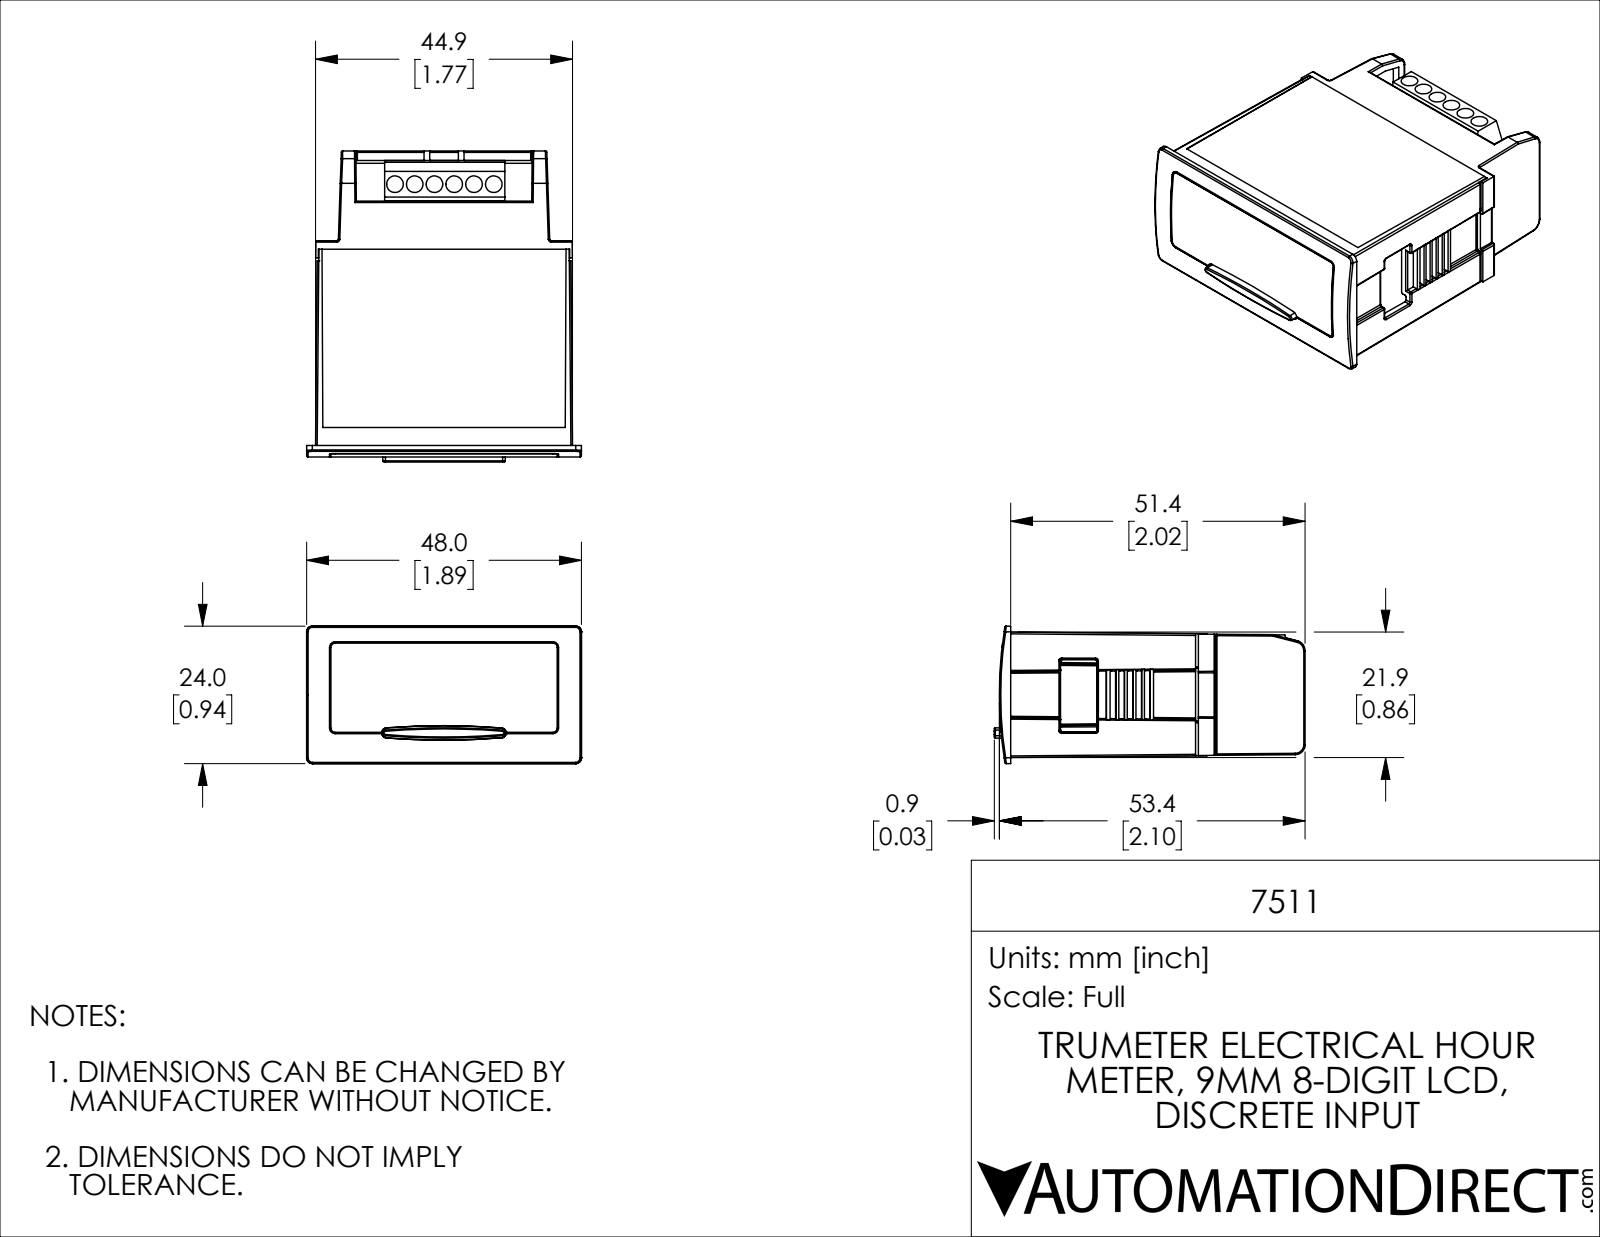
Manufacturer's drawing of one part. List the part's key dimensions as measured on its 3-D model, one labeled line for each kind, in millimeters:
Part name (STEP PRODUCT): 7511
STEP written by: SolidWorks 2021 (CONFIG_CONTROL_DESIGN)
Units: millimetres
Bodies: 2 solids, 1771 faces (1106 planar, 291 cylindrical, 374 other)
Overall size (bounding box): 54.3 × 48 × 24
Volume: 15 500 mm³ · Surface area: 21 700 mm²
Round holes (diameter × count): ⌀2.9 ×6
Round bosses / shafts (diameter × count): ⌀3.8 ×3, ⌀1.8 ×1
Partial cylindrical surfaces — rounded edges, fillets, slot ends (radius × count): R0.3 ×157, R1 ×12, R0.5 ×11, R0.3 ×4, R0.8 ×4, R0.5 ×2, R1.8 ×2, R128.7 ×2
Main face-to-face distances: 20.4, 1.7, 1.8, 42.4, 18.7, 20.4, 1.3, 1.5, 1.1, 43.5
Hole centre spacings: 3.5, 6.9, 10.3, 13.8, 17.2
